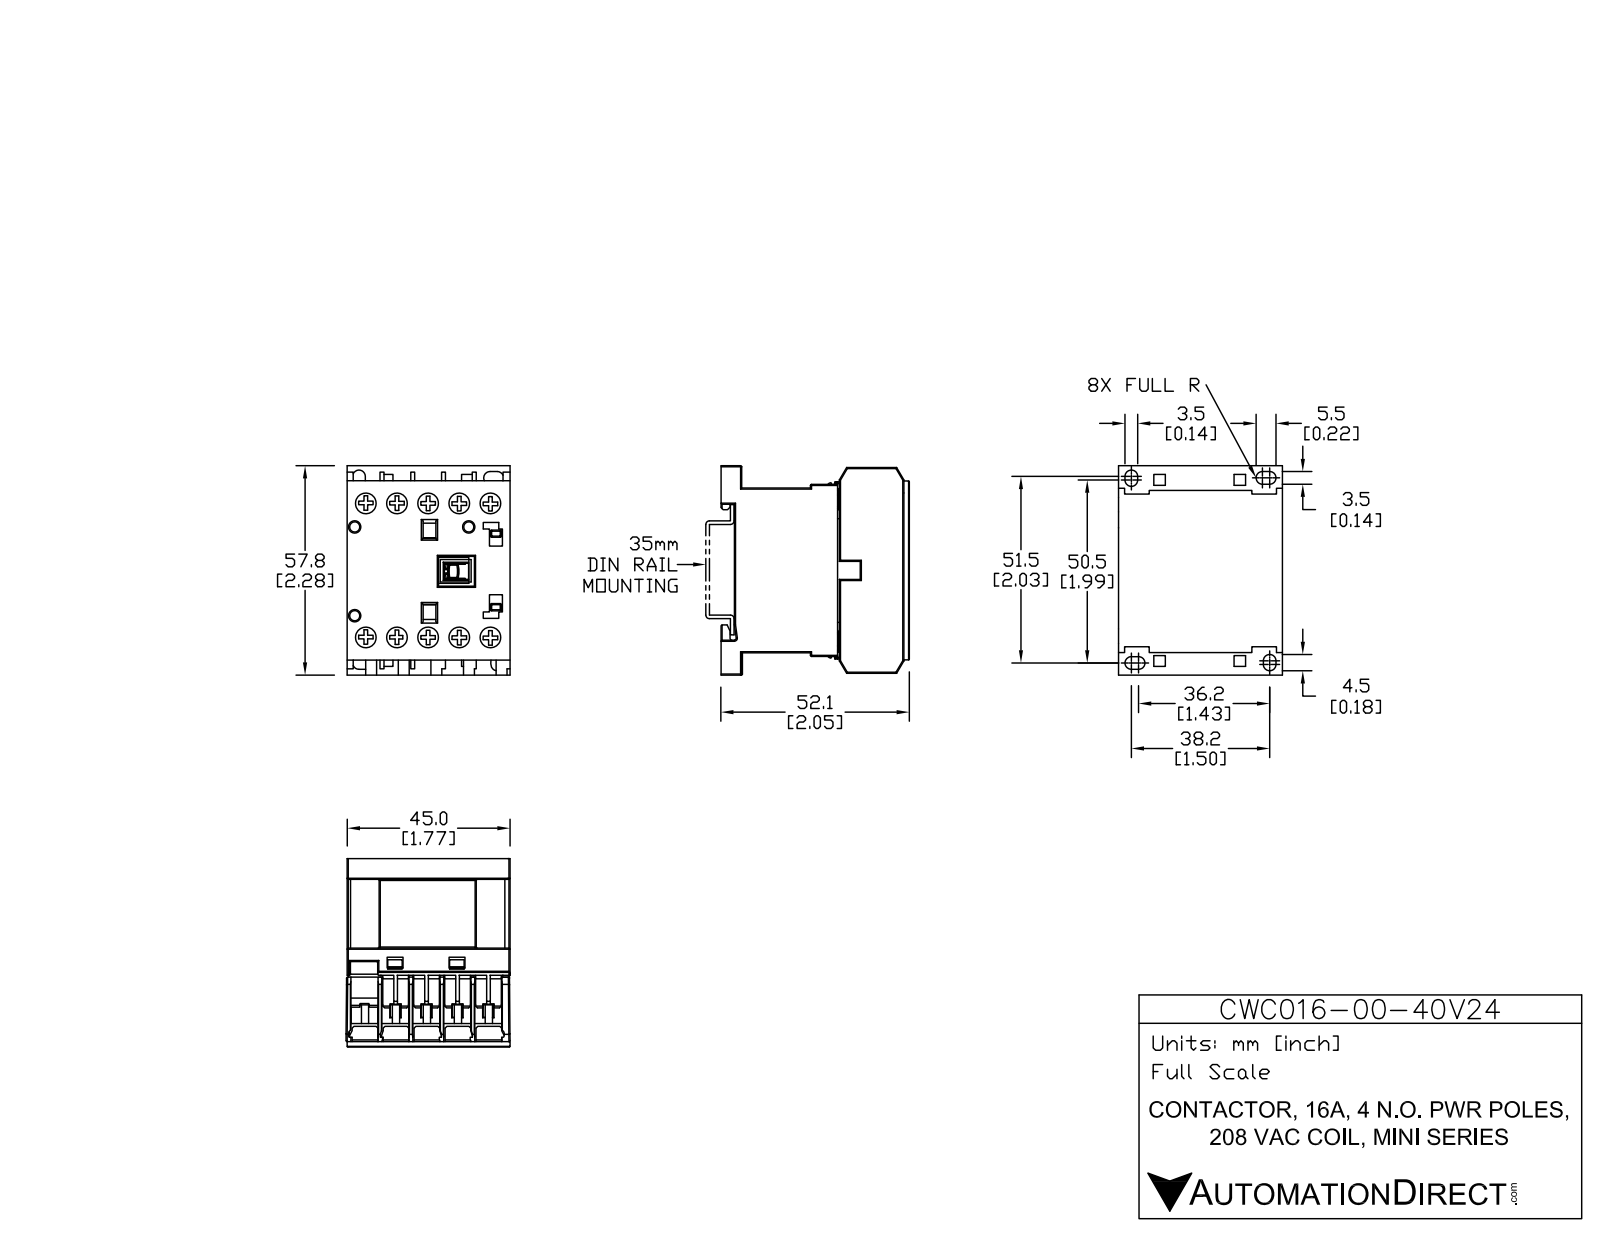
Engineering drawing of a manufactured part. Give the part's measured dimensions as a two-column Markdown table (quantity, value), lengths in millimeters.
| quantity | value |
| --- | --- |
| part name | CWC16-00-40V24 |
| STEP written by | SolidWorks 2013 (AUTOMOTIVE_DESIGN) |
| units | millimeters |
| bodies | 15 solids, 535 faces (445 planar, 90 cylindrical, 0 other) |
| overall size | 58.04 × 52.12 × 45.75 |
| volume | 97 133 mm³ |
| surface area | 30 437 mm² |
| round holes (diameter × count) | 6.2 × 10, 2.8 × 3 |
| round bosses / shafts (diameter × count) | 5.9 × 10 |
| partial cylindrical surfaces (radius × count) | 0.3 × 20, 1.72 × 6, 1.73 × 2, 0.32 × 1, 0.42 × 1, 0.55 × 1 |
| main face-to-face distances | 8.25, 45.5, 1.25, 16.5, 9.5, 5.5, 17.75, 5.13, 10.63, 7 |
| hole center spacings | 8.55, 37.94, 17.1, 40.72, 36.96, 25.65, 44.99, 6.91 |
